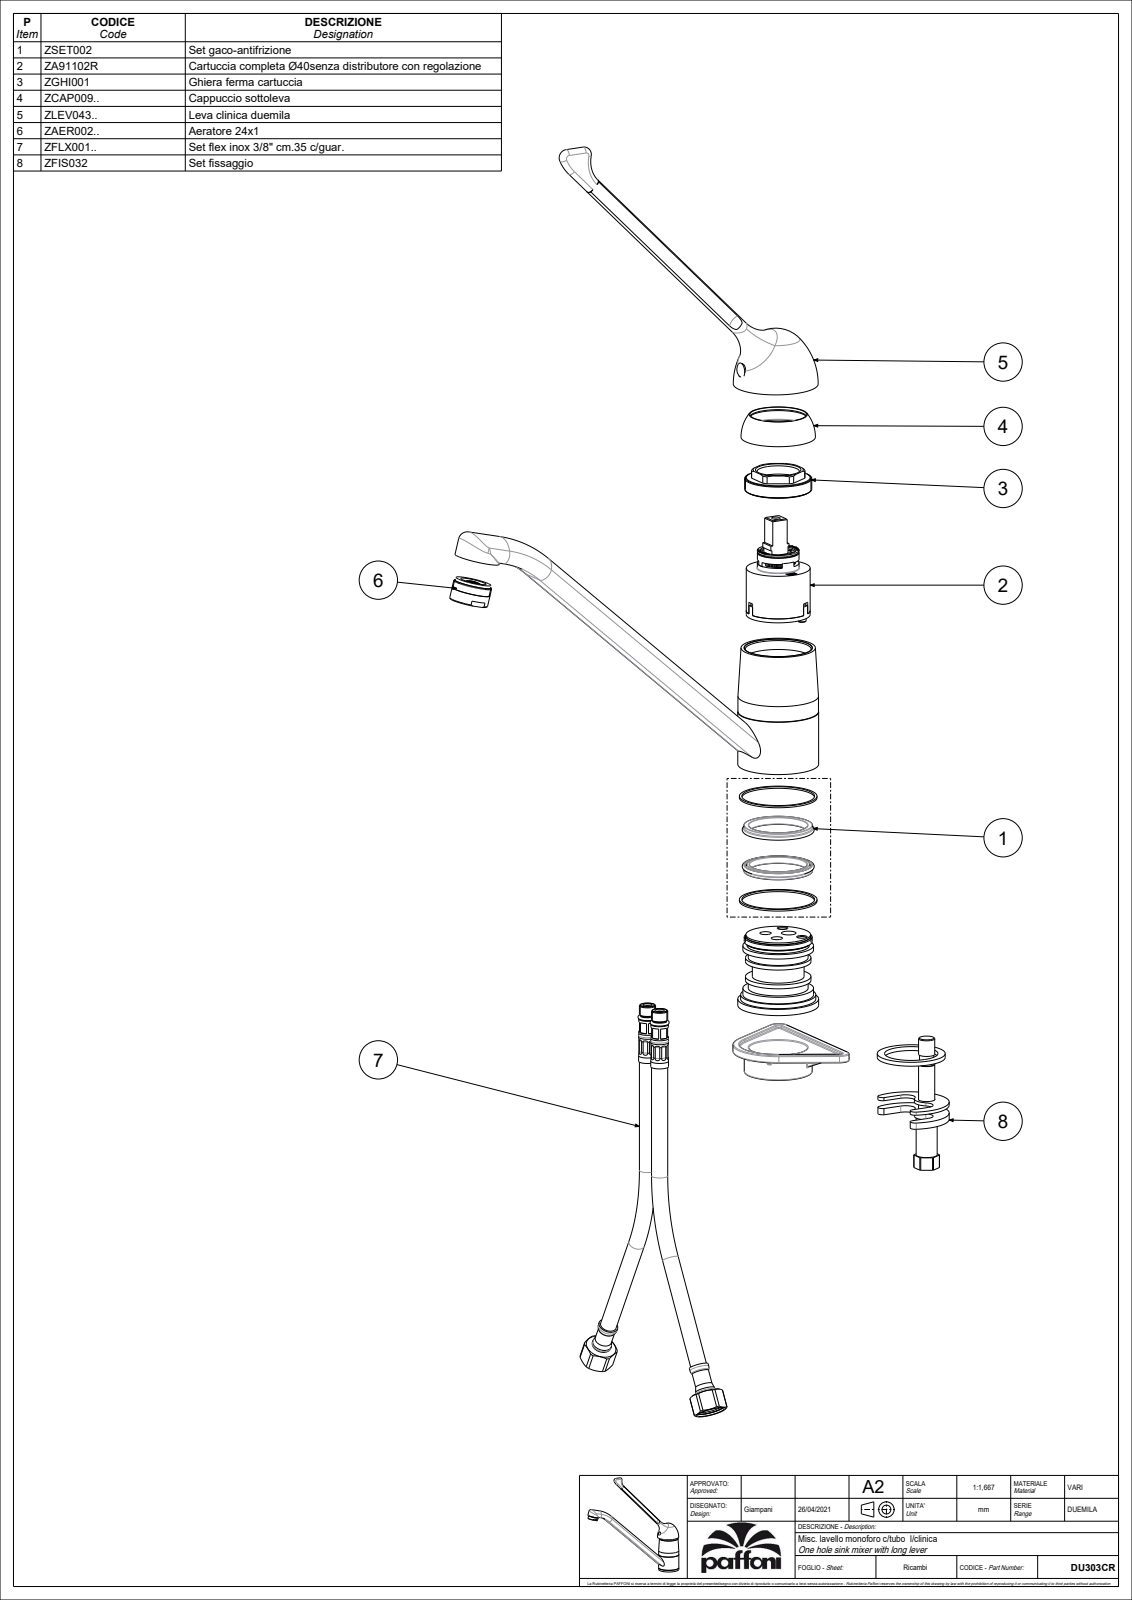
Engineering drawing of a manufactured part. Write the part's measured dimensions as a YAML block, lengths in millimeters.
part_name: "DU303CR"
step_written_by: "CREO PARAMETRIC BY PTC INC, 2020044 (CONFIG_CONTROL_DESIGN)"
units: millimeters
bodies: {solids: 1, faces: 185, planar: 57, cylindrical: 72, other: 56}
overall_size: [253.52, 253.2, 52.5]
volume: 262736
surface_area: 70293
round_holes:
  - {diameter: 9, count: 3}
  - {diameter: 5, count: 1}
  - {diameter: 6, count: 1}
  - {diameter: 35, count: 1}
  - {diameter: 44, count: 1}
  - {diameter: 47.5, count: 1}
  - {diameter: 48.2, count: 1}
round_bosses_or_shafts:
  - {diameter: 50, count: 1}
  - {diameter: 49.8, count: 1}
  - {diameter: 46.5, count: 1}
  - {diameter: 44.8, count: 1}
  - {diameter: 43.7, count: 1}
  - {diameter: 40.5, count: 1}
  - {diameter: 37, count: 1}
  - {diameter: 32, count: 1}
partial_cylinders:
  - {radius: 5.5, count: 4}
  - {radius: 3, count: 2}
  - {radius: 16.5, count: 2}
  - {radius: 24.9, count: 1}
  - {radius: 65, count: 1}
face_to_face_distances: [83.25, 6, 7.5, 17, 10, 19.5, 2.5, 4.8, 10.8, 4]
hole_center_spacings: [0.4, 7.5, 71.8, 72.2]
